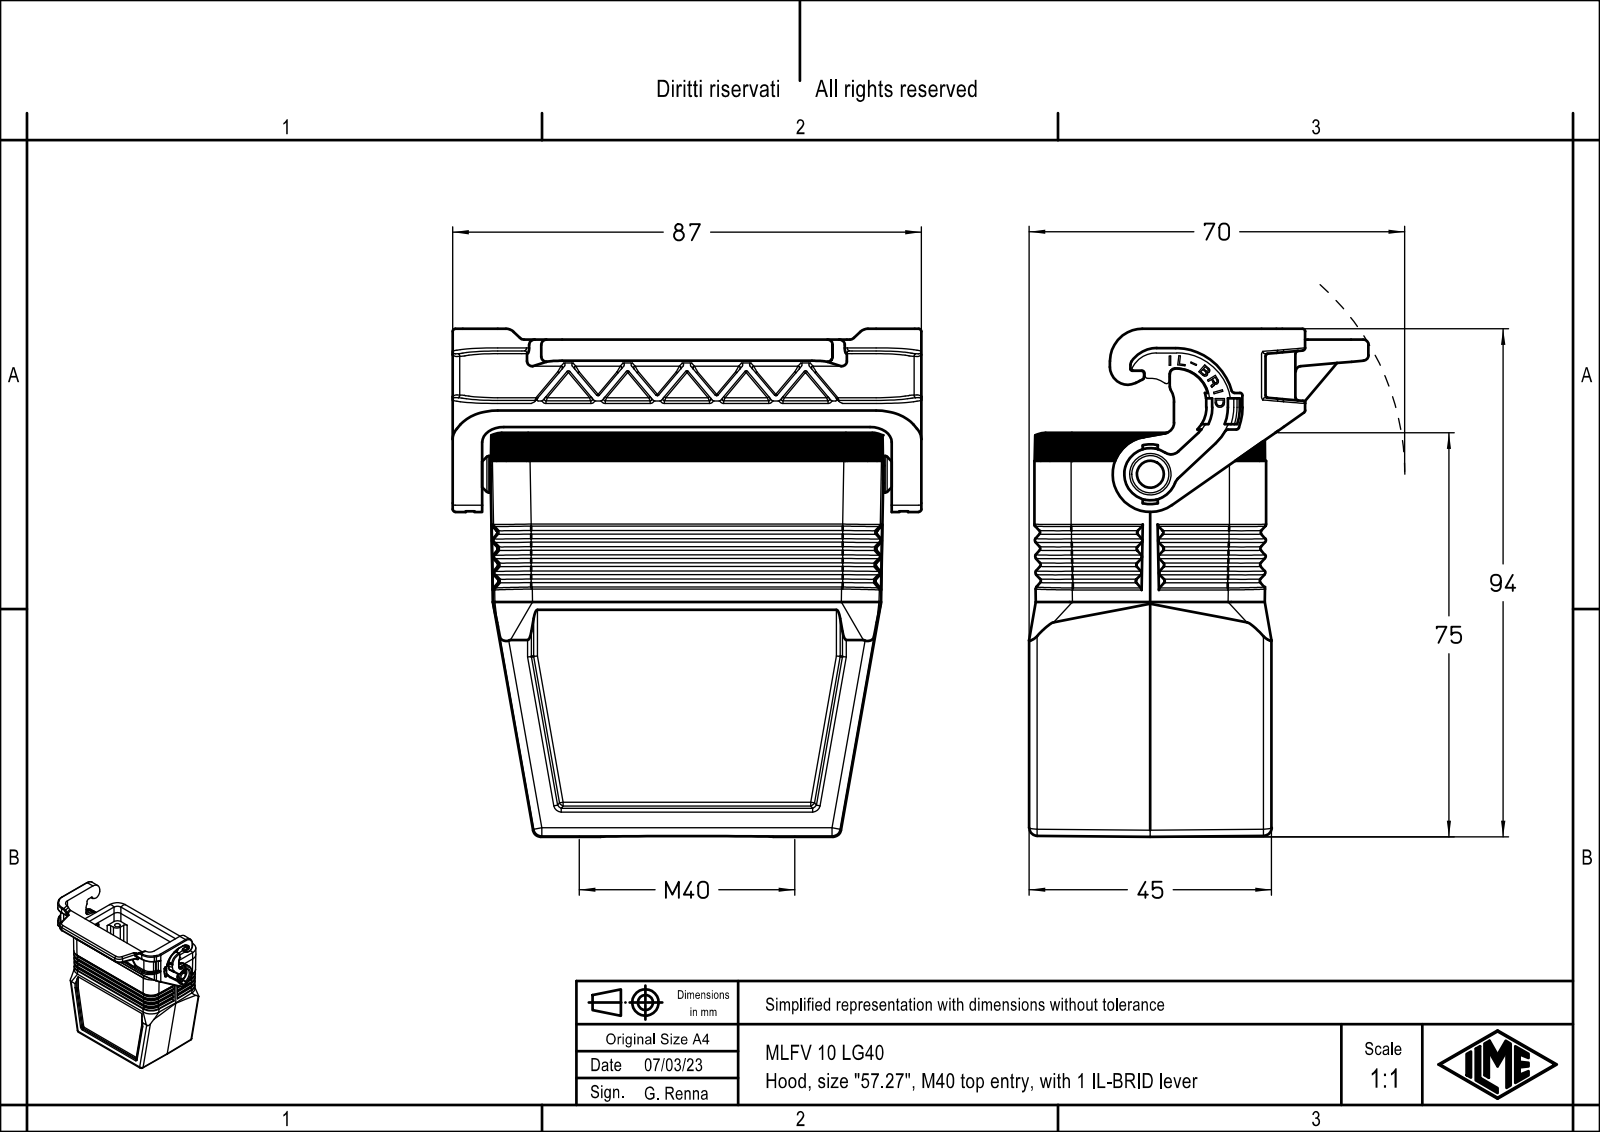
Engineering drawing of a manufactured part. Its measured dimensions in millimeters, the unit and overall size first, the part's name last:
Units: millimetres
Overall size (bounding box): 94.25 × 87 × 63
Round holes (diameter × count): ⌀3 ×4, ⌀3.5 ×4, ⌀3.25 ×1, ⌀5.4 ×1, ⌀7.7 ×1, ⌀38.5 ×1
Round bosses / shafts (diameter × count): ⌀6.9 ×1, ⌀6.8 ×1, ⌀5.2 ×1, ⌀3.2 ×1
Partial cylindrical surfaces — rounded edges, fillets, slot ends (radius × count): R0.1 ×27, R0.5 ×25, R1.5 ×25, R0.2 ×15, R1 ×14, R7 ×14, R0.33 ×13, R3 ×12
Main face-to-face distances: 39.25, 3.75, 43, 1, 4.75, 7, 35.5, 34.5, 38.25, 2
Hole centre spacings: 27, 31.32, 31.75, 57, 63.07
Volume: 83 768 mm³ · Surface area: 45 003 mm²
Bodies: 1 solid, 1218 faces (711 planar, 305 cylindrical, 202 other)
Part name (STEP PRODUCT): MLFV 10 LG32; MLFV 10 LG25; MLFV 10 LG40
STEP written by: Creo Elements/Direct Modeling 20.1B 02-Apr-2019 (C) Parametric Technology GmbH (AUTOMOTIVE_DESIGN)
